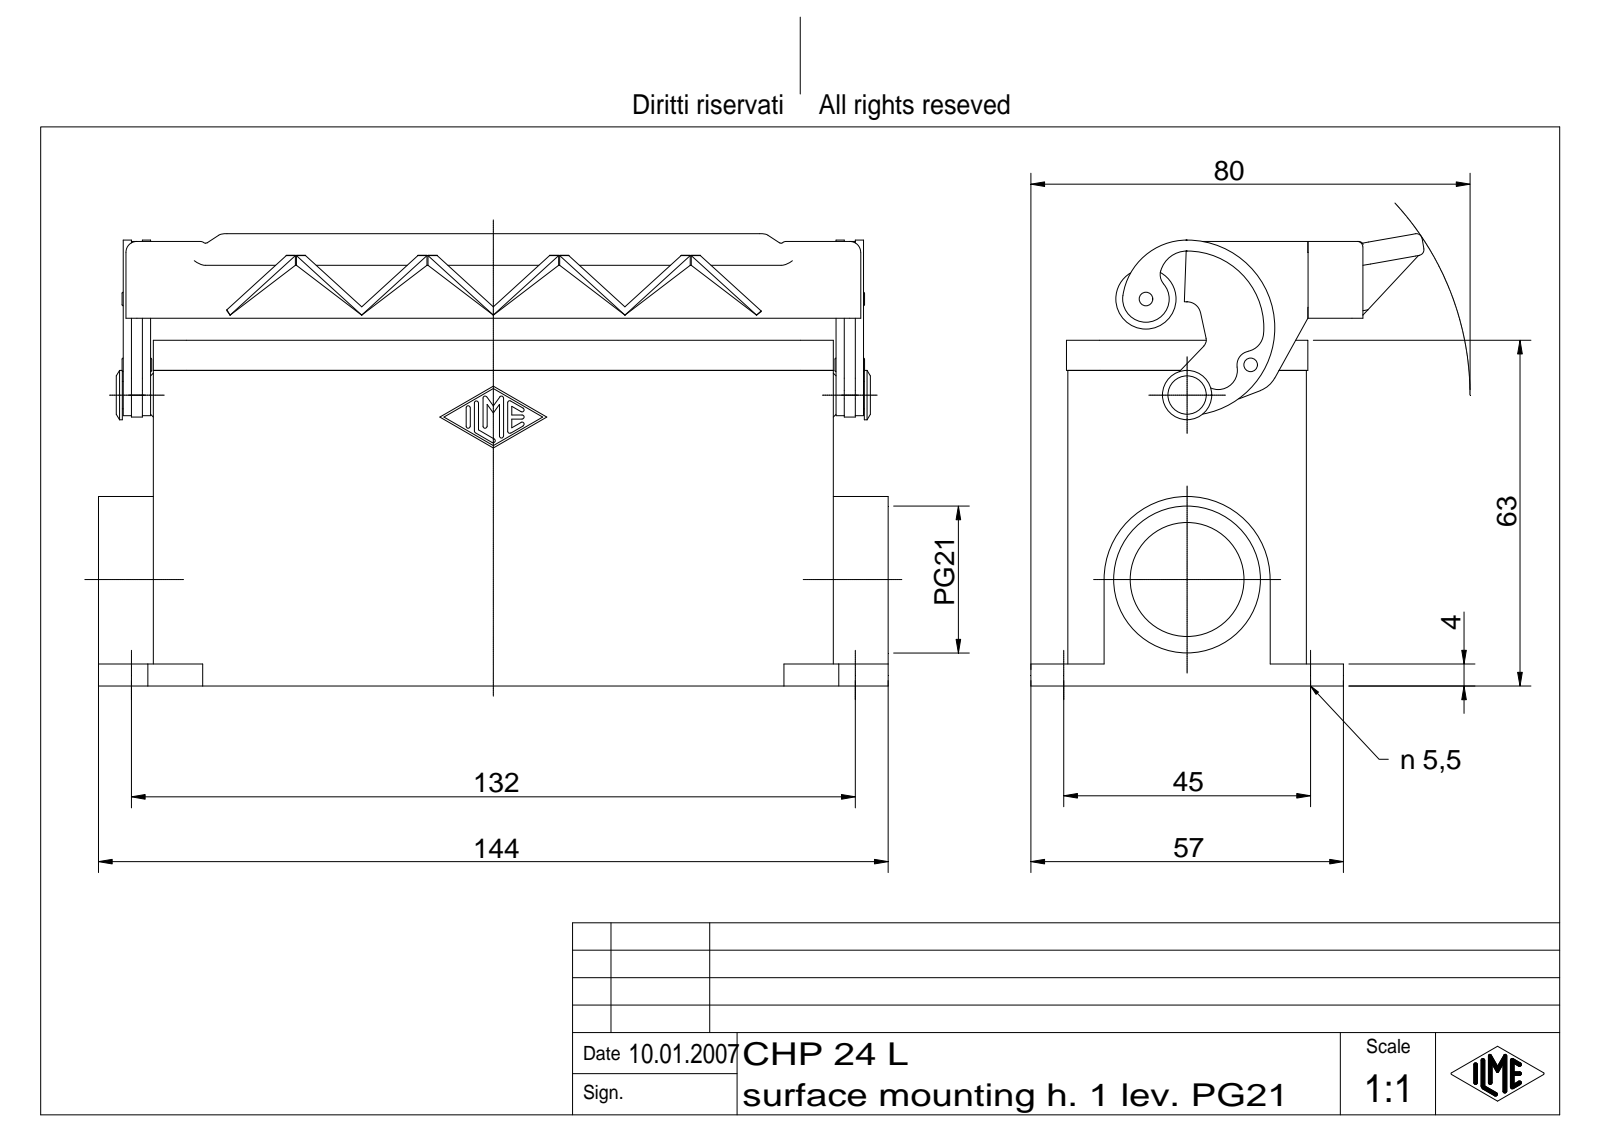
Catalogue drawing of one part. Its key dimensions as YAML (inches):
part_name: "CHP 24 L"
step_written_by: "Autodesk Inventor 7 (AUTOMOTIVE_DESIGN)"
units: inches
bodies: {solids: 4, faces: 463, planar: 191, cylindrical: 123, other: 149}
overall_size: [5.669, 3.245, 2.823]
volume: 7.782
surface_area: 112.5
round_holes:
  - {diameter: 0.217, count: 4}
  - {diameter: 0.079, count: 1}
  - {diameter: 0.818, count: 1}
  - {diameter: 1.054, count: 1}
round_bosses_or_shafts:
  - {diameter: 0.433, count: 1}
  - {diameter: 0.354, count: 1}
  - {diameter: 0.197, count: 1}
  - {diameter: 0.118, count: 1}
  - {diameter: 0.098, count: 1}
partial_cylinders:
  - {radius: 0.015, count: 14}
  - {radius: 0.079, count: 12}
  - {radius: 0.236, count: 8}
  - {radius: 0.039, count: 7}
  - {radius: 0.059, count: 5}
  - {radius: 0.118, count: 4}
  - {radius: 0.098, count: 3}
  - {radius: 0.138, count: 2}
face_to_face_distances: [0.118, 1.594, 0.157, 1.713, 1.476, 0.128, 0.03, 2.264, 2.106, 0.413]
hole_center_spacings: [1.772, 5.197, 5.491, 1.606]
